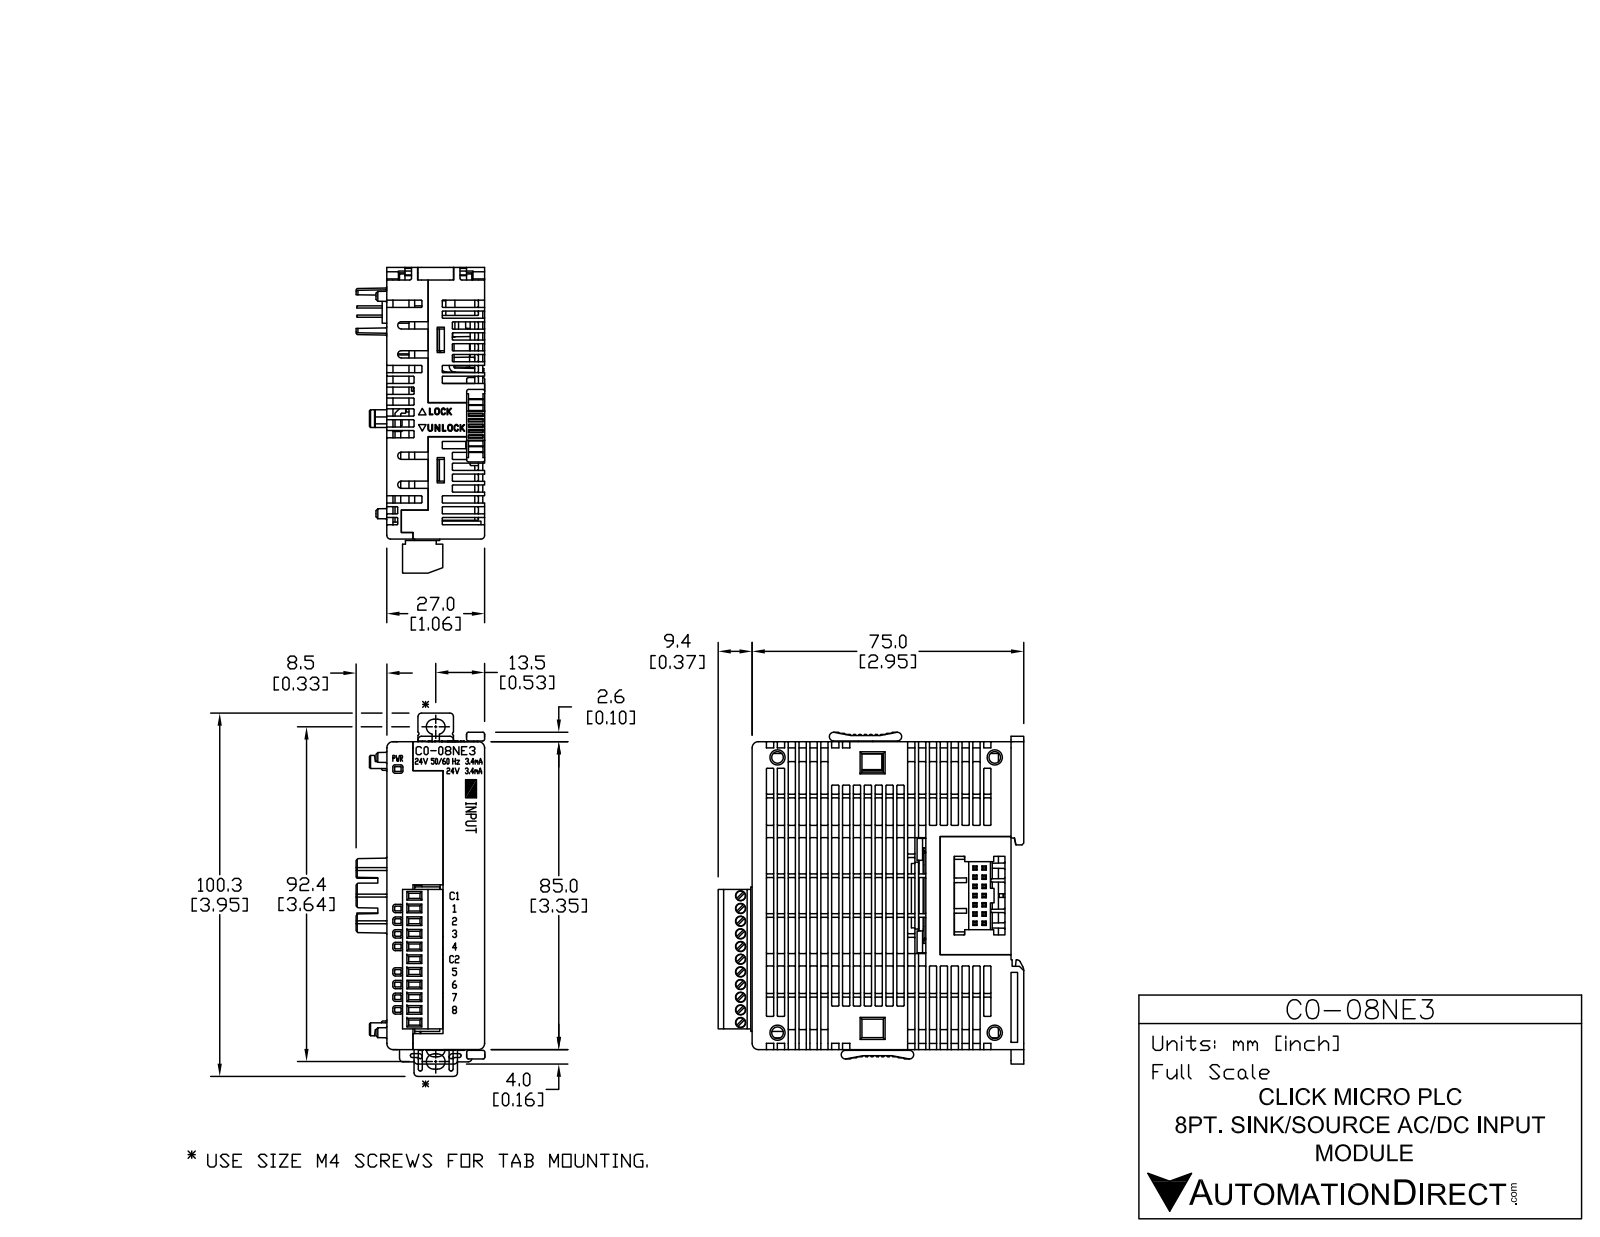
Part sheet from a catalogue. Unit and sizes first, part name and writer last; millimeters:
Units: millimetres
Overall size (bounding box): 91.6 × 84.4 × 35.55
Round holes (diameter × count): ⌀1 ×11, ⌀2.8 ×11, ⌀3.2 ×4, ⌀2 ×2
Round bosses / shafts (diameter × count): ⌀2.6 ×11, ⌀1.9 ×1
Partial cylindrical surfaces — rounded edges, fillets, slot ends (radius × count): R0.2 ×570, R0.5 ×43, R0.3 ×22, R1 ×18, R1.2 ×12, R2.8 ×11, R1.7 ×6, R2.1 ×4
Main face-to-face distances: 27.01, 0.5, 0.51, 26.5, 71.5, 1.7, 85, 26.3, 26.81, 84.5
Hole centre spacings: 3.5, 7, 10.5, 14, 17.5, 21, 24.5, 28
Volume: 162 508 mm³ · Surface area: 31 791 mm²
Bodies: 1 solid, 3733 faces (2680 planar, 927 cylindrical, 126 other)
Part name (STEP PRODUCT): C0-08NE3
STEP written by: SolidWorks 2011 (AUTOMOTIVE_DESIGN)
